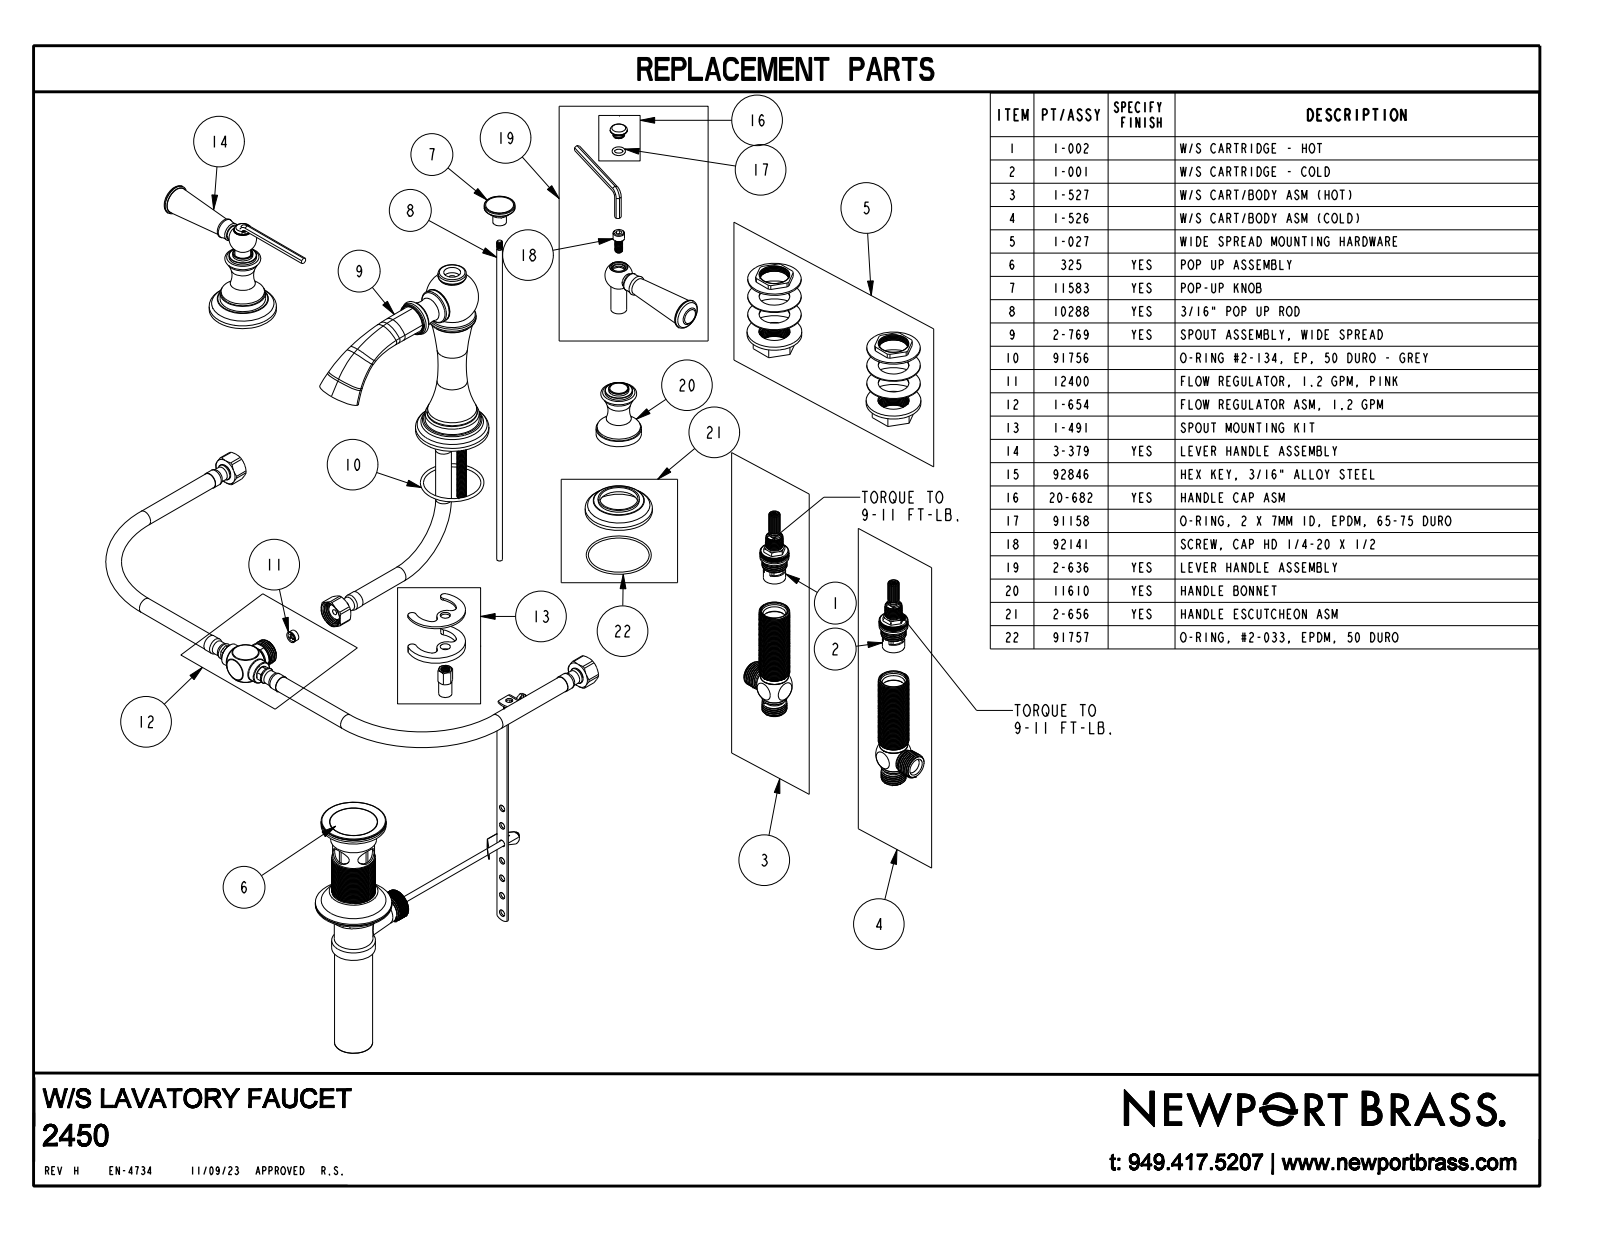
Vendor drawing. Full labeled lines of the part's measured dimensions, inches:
Part name (STEP PRODUCT): 2450
STEP written by: CREO PARAMETRIC BY PTC INC, 2018400 (CONFIG_CONTROL_DESIGN)
Units: inches
Bodies: 3 solids, 283 faces (39 planar, 62 cylindrical, 182 other)
Overall size (bounding box): 14.6 × 6.887 × 6.793
Volume: 22.04 in³ · Surface area: 103 in²
Round holes (diameter × count): ⌀0.55 ×1, ⌀0.985 ×1
Round bosses / shafts (diameter × count): ⌀2.2 ×2, ⌀1.49 ×2, ⌀1.42 ×2, ⌀0.9 ×2, ⌀0.66 ×2, ⌀0.56 ×2, ⌀0.517 ×2, ⌀2.4 ×1
Partial cylindrical surfaces — rounded edges, fillets, slot ends (radius × count): R0.092 ×3, R0.092 ×1
Main face-to-face distances: 0.43, 0.08, 2.17, 1.74, 2.09, 1.66, 0.21, 5.687, 0.64, 1.45
